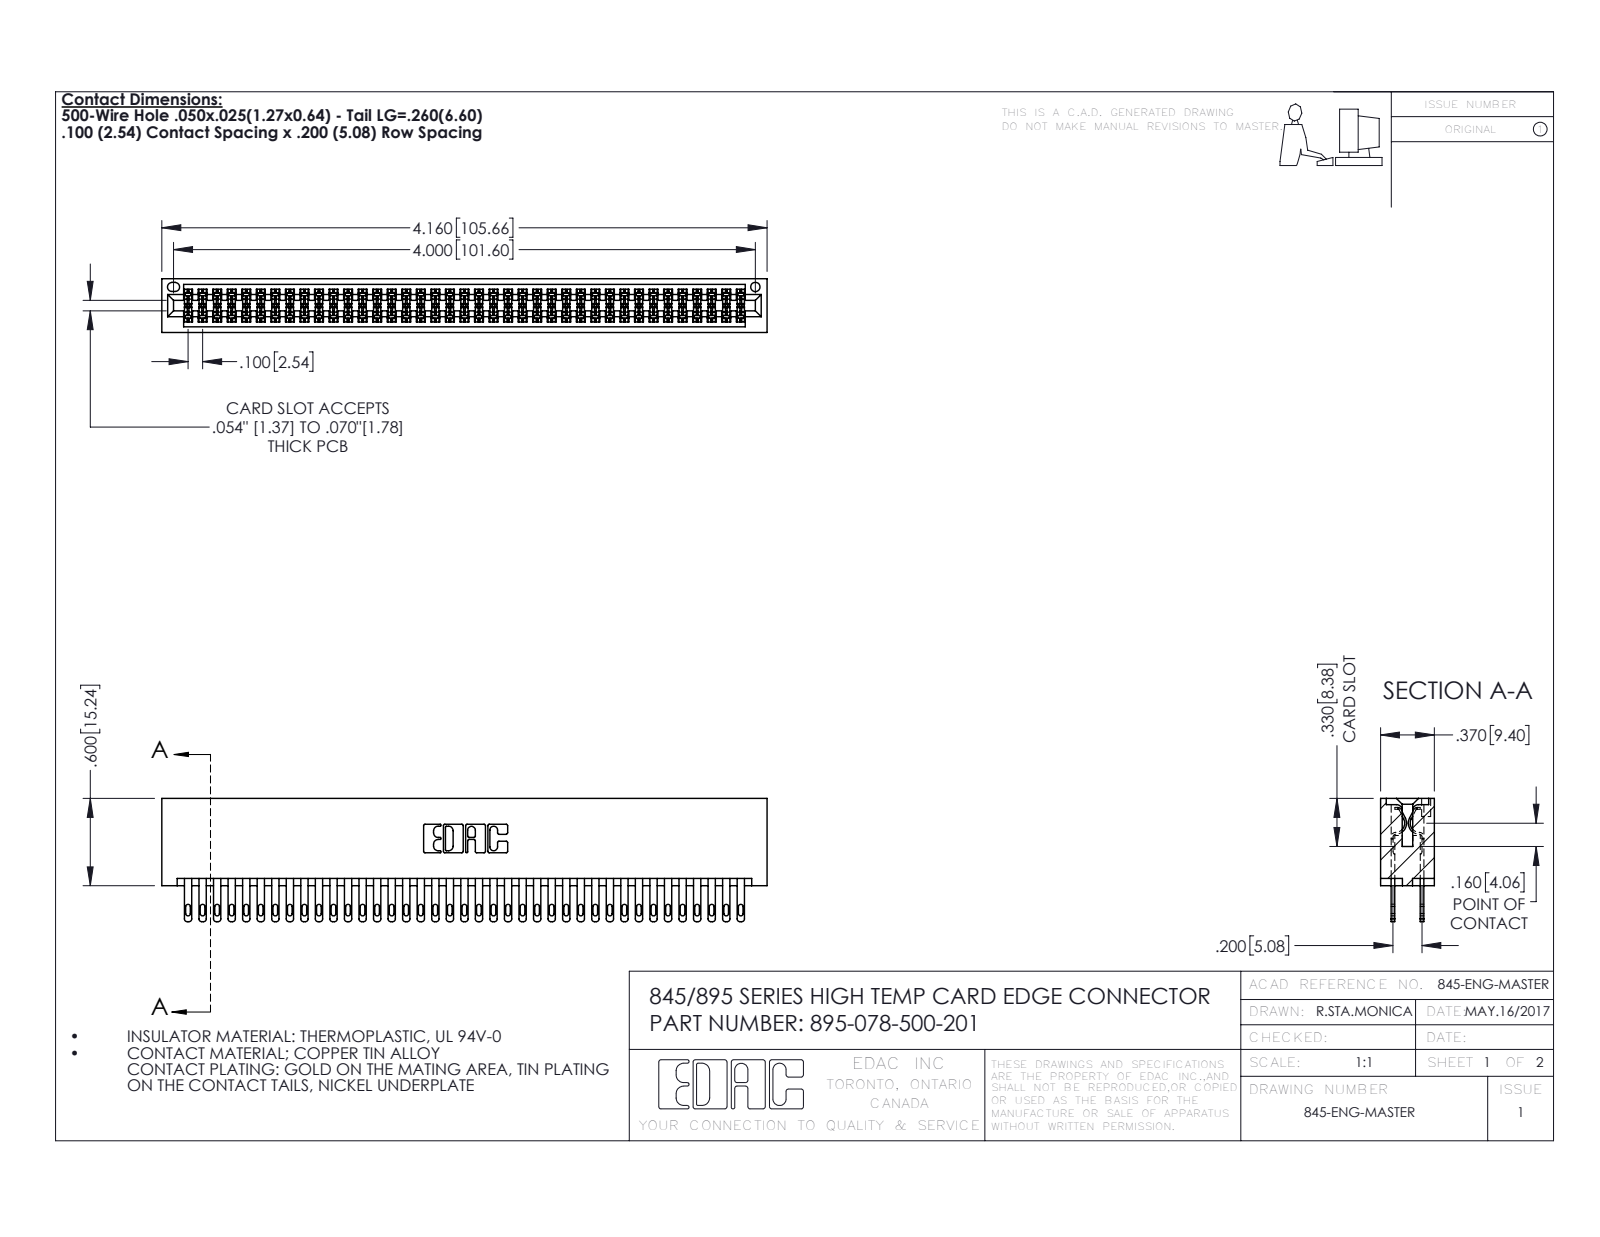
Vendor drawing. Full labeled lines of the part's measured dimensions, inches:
Part name (STEP PRODUCT): 345-292-001_345-293-100; 345 Part_No Mounting Lugs; 345-078-500-201
STEP written by: SolidWorks 2016 (CONFIG_CONTROL_DESIGN)
Units: inches
Bodies: 79 solids, 3706 faces (2182 planar, 1524 cylindrical, 0 other)
Overall size (bounding box): 4.16 × 0.847 × 0.37
Volume: 0.677 in³ · Surface area: 27.02 in²
Round holes (diameter × count): ⌀0.064 ×1
Partial cylindrical surfaces — rounded edges, fillets, slot ends (radius × count): R0.006 ×117, R0.016 ×78, R0.02 ×78, R0.01 ×22, R0.007 ×6, R0.031 ×6, R0.026 ×3, R0.014 ×2
Main face-to-face distances: 0.298, 0.072, 0.2, 0.098, 0.272, 0.025, 0.37, 0.225, 0.175, 0.149
